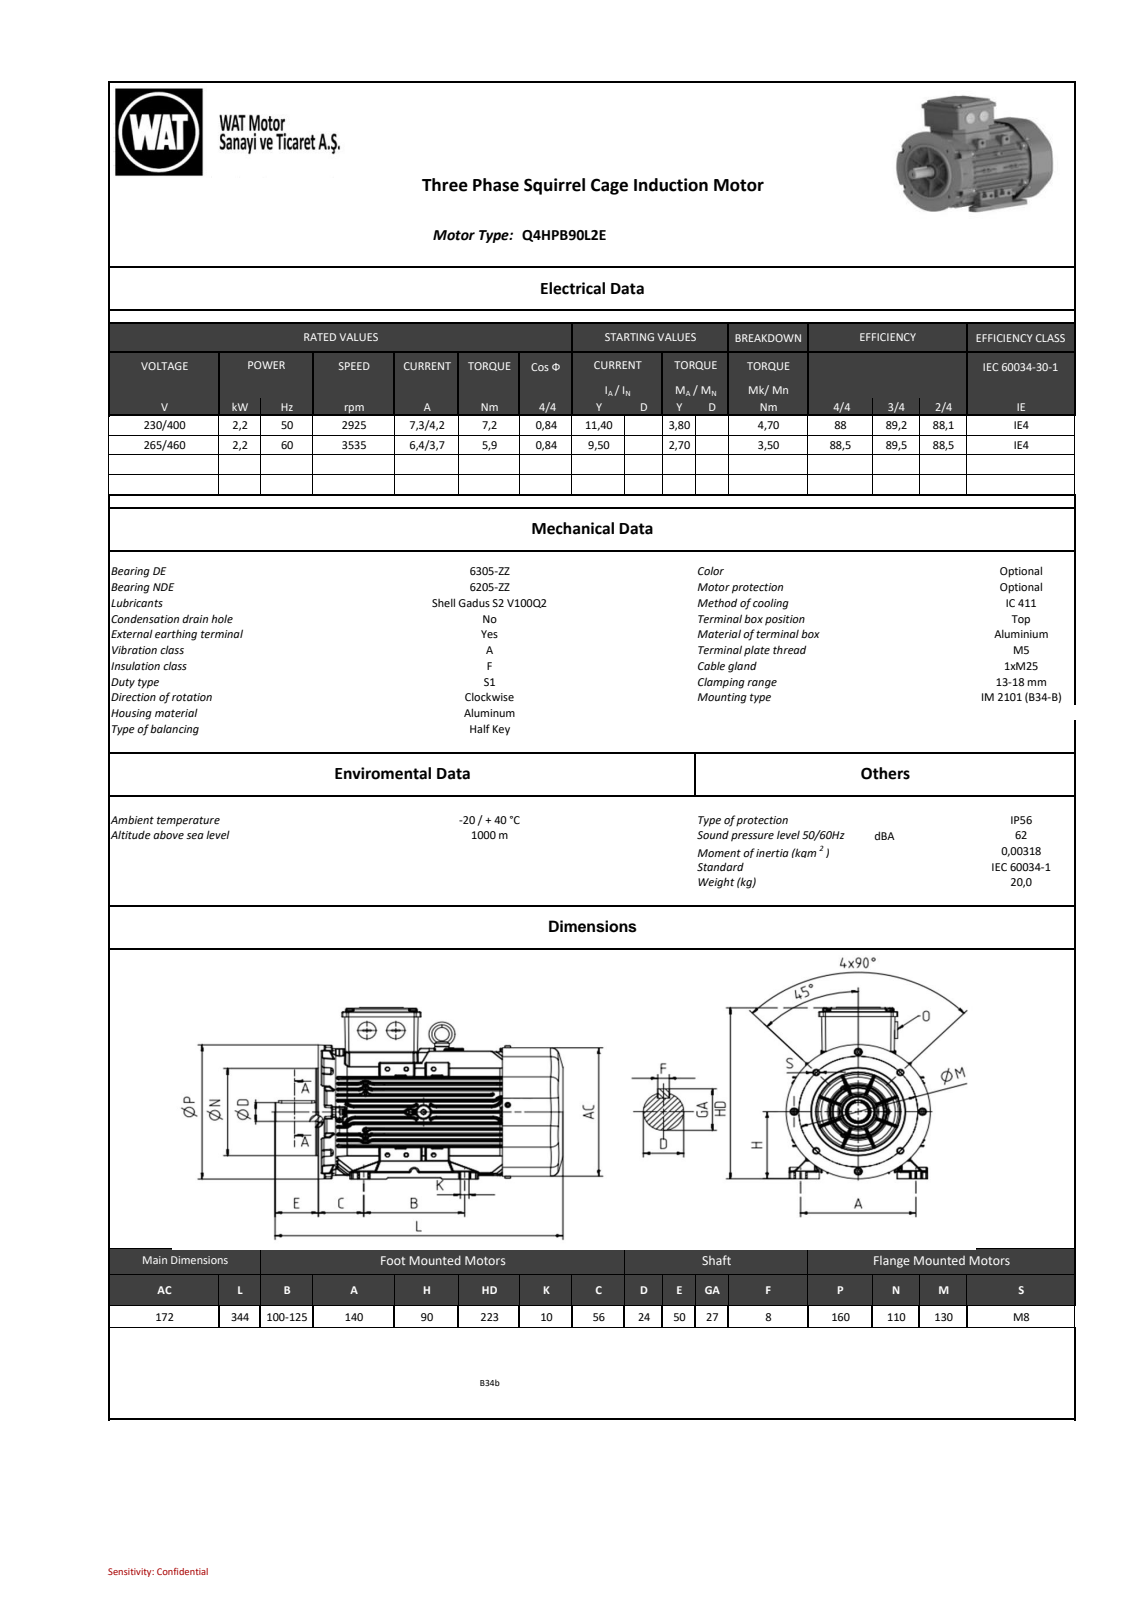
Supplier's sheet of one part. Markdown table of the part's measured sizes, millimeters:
| quantity | value |
| --- | --- |
| part name | model1 |
| STEP written by | SIEMENS PLM Software NX2206.8101 (AUTOMOTIVE_DESIGN) |
| units | millimeters |
| bodies | 0 solids, 6599 faces (1534 planar, 2826 cylindrical, 2239 other) |
| overall size | 343.54 × 223.14 × 178.35 |
| round holes (diameter × count) | 6.8 × 4, 9.87 × 1, 37.42 × 1, 79.79 × 1, 97.79 × 1, 115.78 × 1 |
| round bosses / shafts (diameter × count) | 5 × 8, 8 × 7, 10 × 5, 25 × 3, 110 × 1, 102.19 × 1, 84.19 × 1, 39.5 × 1 |
| partial cylindrical surfaces (radius × count) | 1 × 864, 0.8 × 532, 0.5 × 147, 0.98 × 111, 2 × 95, 8 × 28, 1.5 × 26, 4 × 10 |
| main face-to-face distances | 7.5, 91.91, 8.93, 82.98, 23.57, 50.35, 7.37, 9.06, 90.35, 75.04 |
| hole center spacings | 91.93, 64.98, 65.03, 64.94, 65, 65.02, 65.06, 130 |
